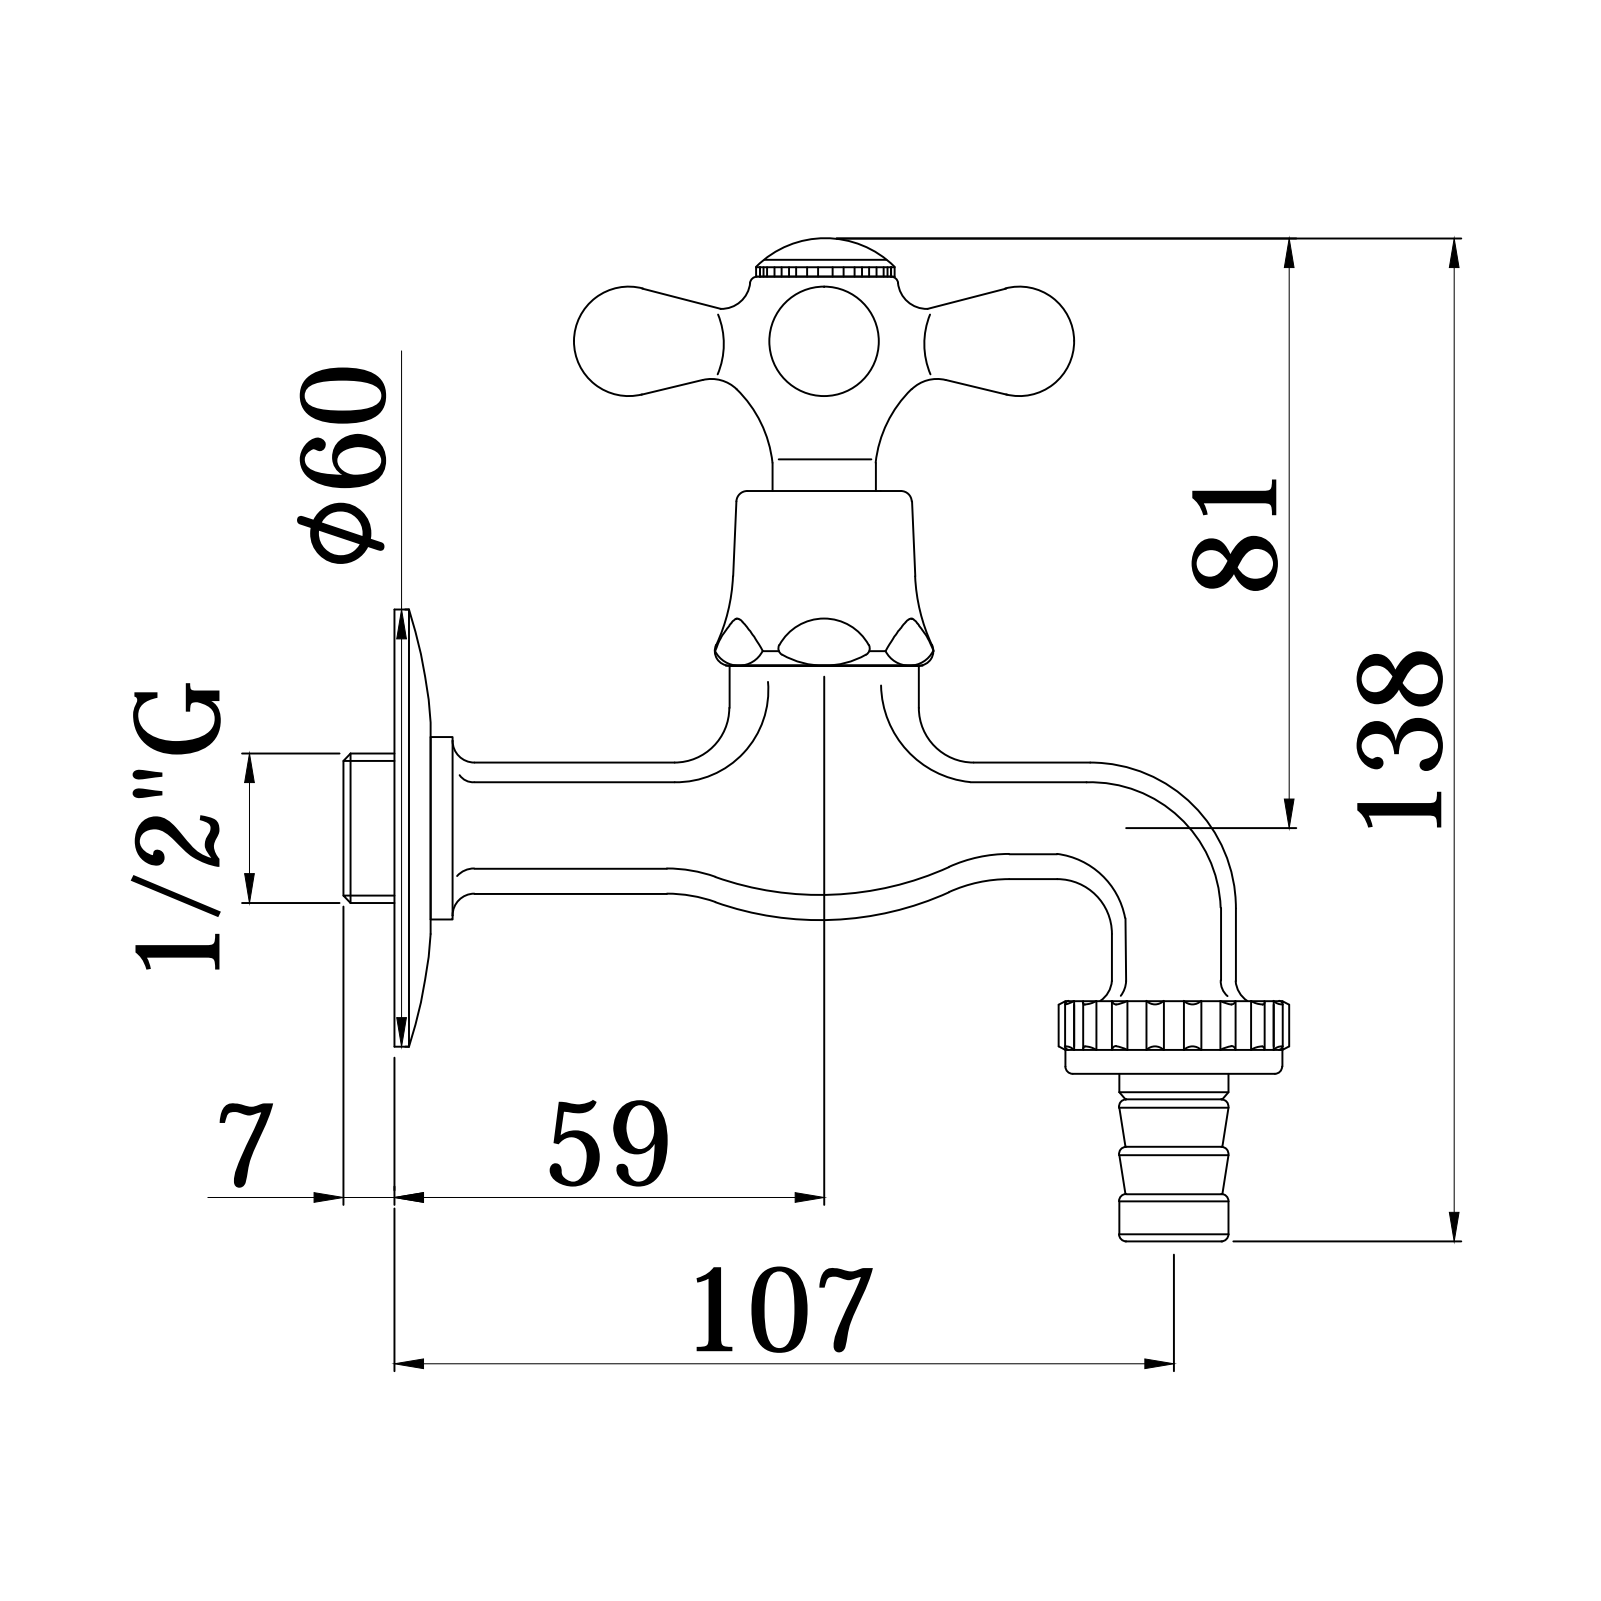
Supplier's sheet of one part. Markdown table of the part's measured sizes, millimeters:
| quantity | value |
| --- | --- |
| part name | IRV211CR |
| STEP written by | CREO PARAMETRIC BY PTC INC, 2020044 (CONFIG_CONTROL_DESIGN) |
| units | millimeters |
| bodies | 1 solid, 209 faces (20 planar, 38 cylindrical, 151 other) |
| overall size | 139.94 × 129.8 × 72 |
| volume | 115 129 mm³ |
| surface area | 25 993 mm² |
| round bosses / shafts (diameter × count) | 58 × 1, 27.5 × 1, 26.5 × 1, 24.7 × 1, 21 × 1, 18 × 1, 13.5 × 1 |
| partial cylindrical surfaces (radius × count) | 1.05 × 18, 14.5 × 1 |
| main face-to-face distances | 26.5, 7.7, 81.75, 23.49, 105.24, 53.25, 45.55, 79.75, 72.05, 33.49 |
